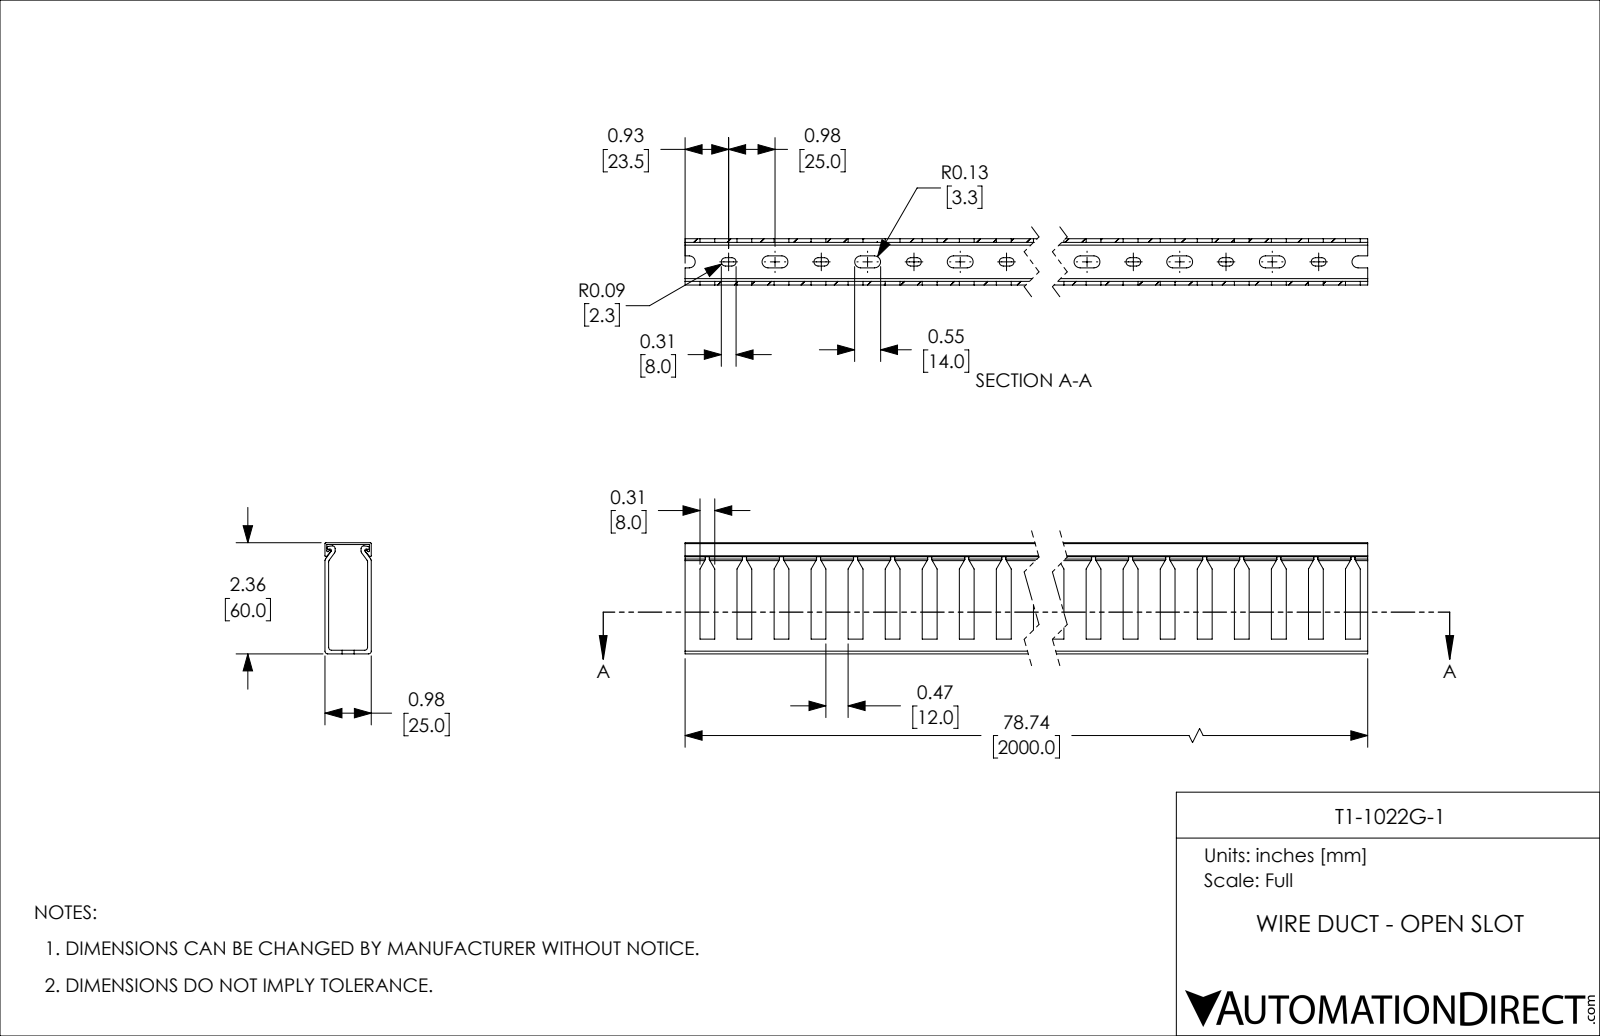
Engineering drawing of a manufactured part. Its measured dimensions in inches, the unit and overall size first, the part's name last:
Units: inches
Overall size (bounding box): 78.74 × 2.362 × 0.984
Partial cylindrical surfaces — rounded edges, fillets, slot ends (radius × count): R0.089 ×80, R0.128 ×80, R0.059 ×12, R0.02 ×8, R0.03 ×6
Main face-to-face distances: 0.079, 0.906, 0.984, 0.827, 0.039, 2.362, 2.323, 2.244, 2.283, 0.945
Volume: 38.83 in³ · Surface area: 1 129 in²
Bodies: 2 solids, 945 faces (514 planar, 431 cylindrical, 0 other)
Part name (STEP PRODUCT): T1-1022G-1
STEP written by: SolidWorks 2021 (CONFIG_CONTROL_DESIGN)
